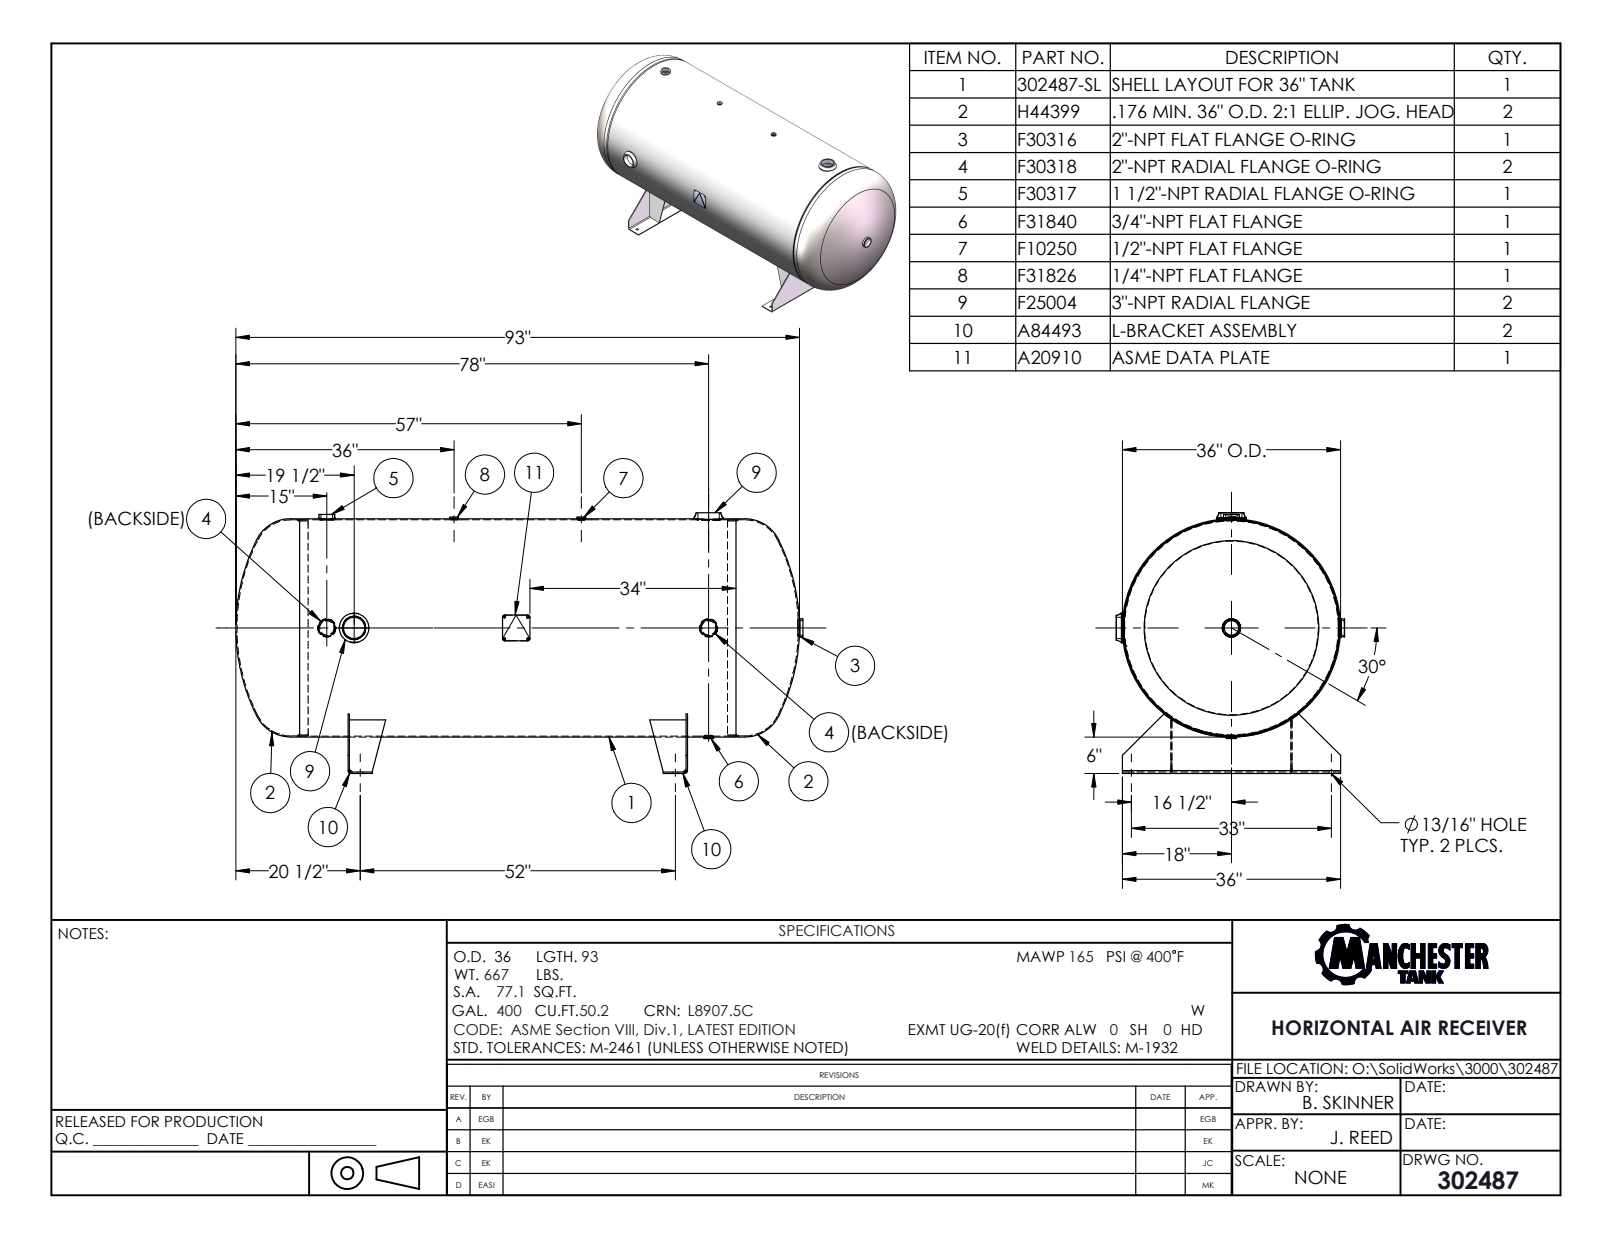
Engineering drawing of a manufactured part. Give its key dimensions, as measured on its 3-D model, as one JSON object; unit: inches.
{"part_name": "302487", "step_written_by": "SolidWorks 2011 (CONFIG_CONTROL_DESIGN)", "units": "inches", "bodies": {"solids": 0, "faces": 203, "planar": 54, "cylindrical": 69, "other": 80}, "overall_size": [93.625, 43, 37.862], "round_holes": [[0.813, 4], [2.375, 3], [3.5, 2], [0.54, 1], [0.84, 1], [1.05, 1], [1.9, 1], [35.276, 1], [35.59, 1]], "round_bosses_or_shafts": [[4.875, 2], [3.625, 2], [36, 1], [35.62, 1], [3.5, 1], [2.875, 1], [2.688, 1], [2.063, 1]], "partial_cylinders_radius": [[0.094, 2], [0.344, 2], [18.06, 1]], "face_to_face_distances": [0.25, 55.75, 56, 55.5, 20, 0.25, 8, 8.25, 63.75, 64], "hole_center_spacings": [17.393, 22.639, 40.056, 59.82, 21, 33, 42, 52]}
